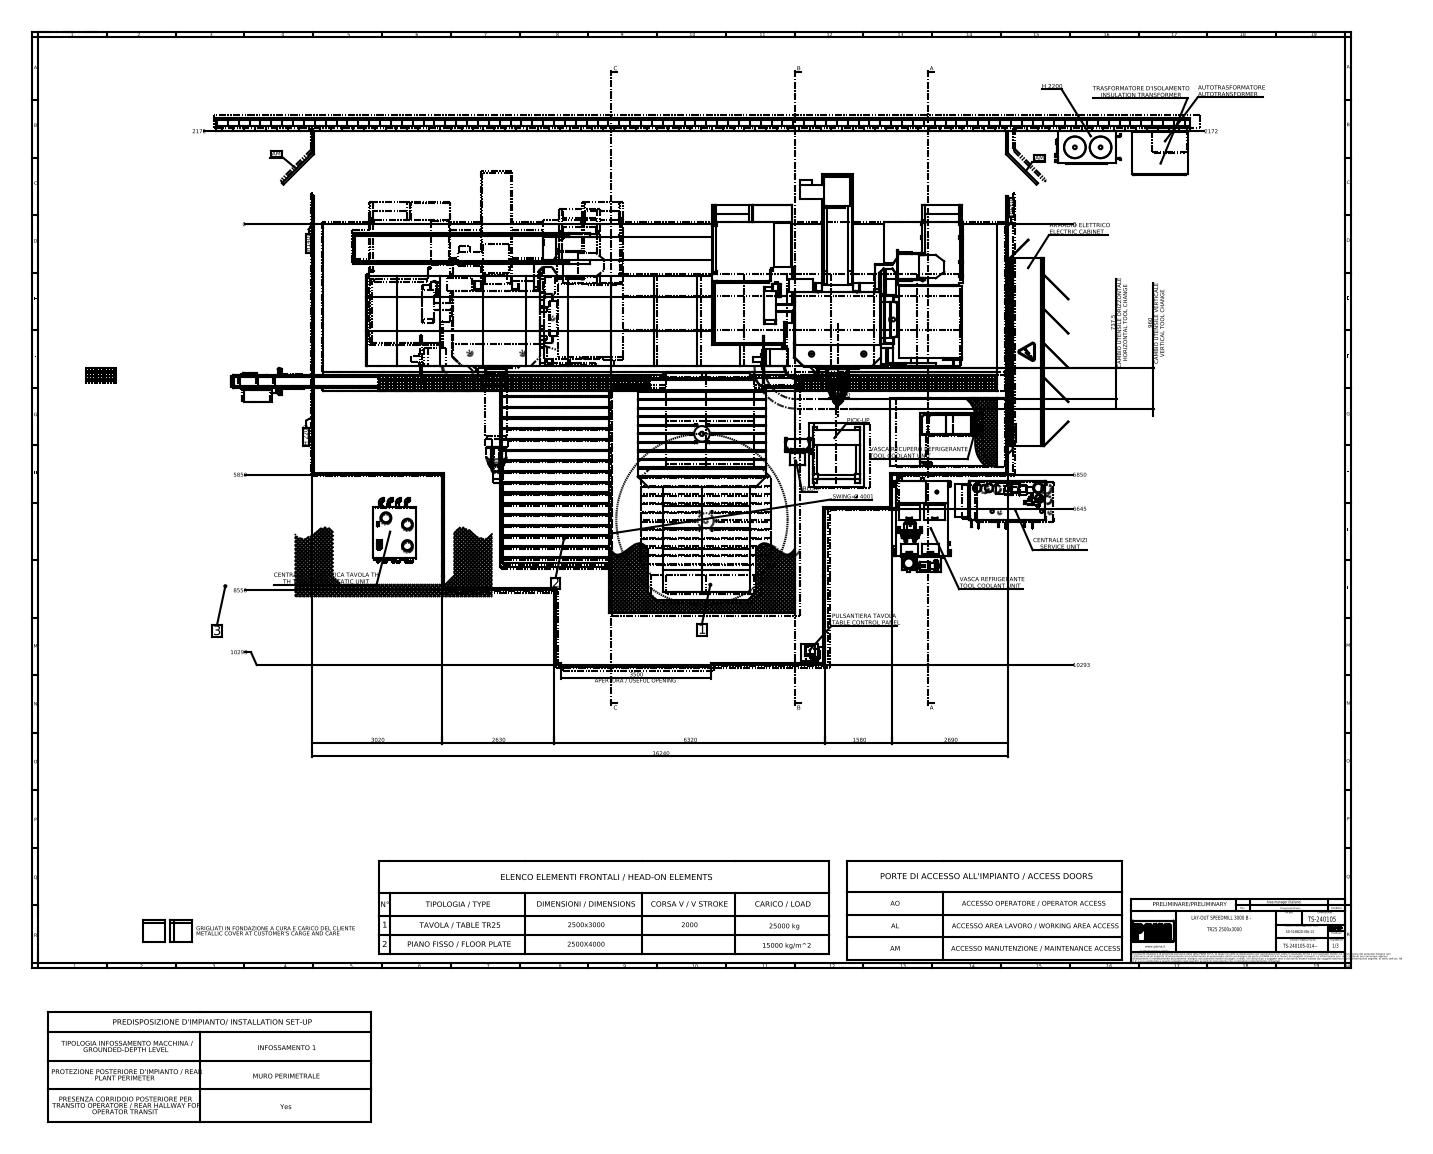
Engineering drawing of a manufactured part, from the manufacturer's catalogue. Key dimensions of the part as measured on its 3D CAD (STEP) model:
Part name (STEP PRODUCT): S003502_TM 2R H3950; S003174_Y=3500; S003545_Y=3500; S001798_CORSA V=0; B=0° (+8 more)
STEP written by: SolidWorks 2023 (AUTOMOTIVE_DESIGN)
Units: millimetres
Bodies: 566 solids, 8487 faces (6420 planar, 1656 cylindrical, 411 other)
Overall size (bounding box): 22740 × 15715 × 9400
Volume: 753 200 000 000 mm³ · Surface area: 2 417 000 000 mm²
Round holes (diameter × count): ⌀35 ×102, ⌀69.6 ×63, ⌀13 ×16, ⌀14 ×8, ⌀8 ×6, ⌀32 ×6, ⌀12 ×5, ⌀6.8 ×4, ⌀7 ×4, ⌀12.5 ×4, ⌀50 ×3, ⌀56.66 ×3
Round bosses / shafts (diameter × count): ⌀20 ×14, ⌀9 ×10, ⌀55 ×8, ⌀30 ×8, ⌀66.3 ×7, ⌀60 ×7, ⌀35 ×6, ⌀200 ×5
Partial cylindrical surfaces — rounded edges, fillets, slot ends (radius × count): R5 ×239, R10 ×77, R15 ×48, R6 ×36, R2 ×28, R35 ×26, R8 ×18, R20 ×15
Main face-to-face distances: 2000, 300, 50, 450, 1550, 15715, 15415, 22740, 100, 1950
Hole centre spacings: 250, 500, 750, 1000, 1250, 1500, 1750, 2000
